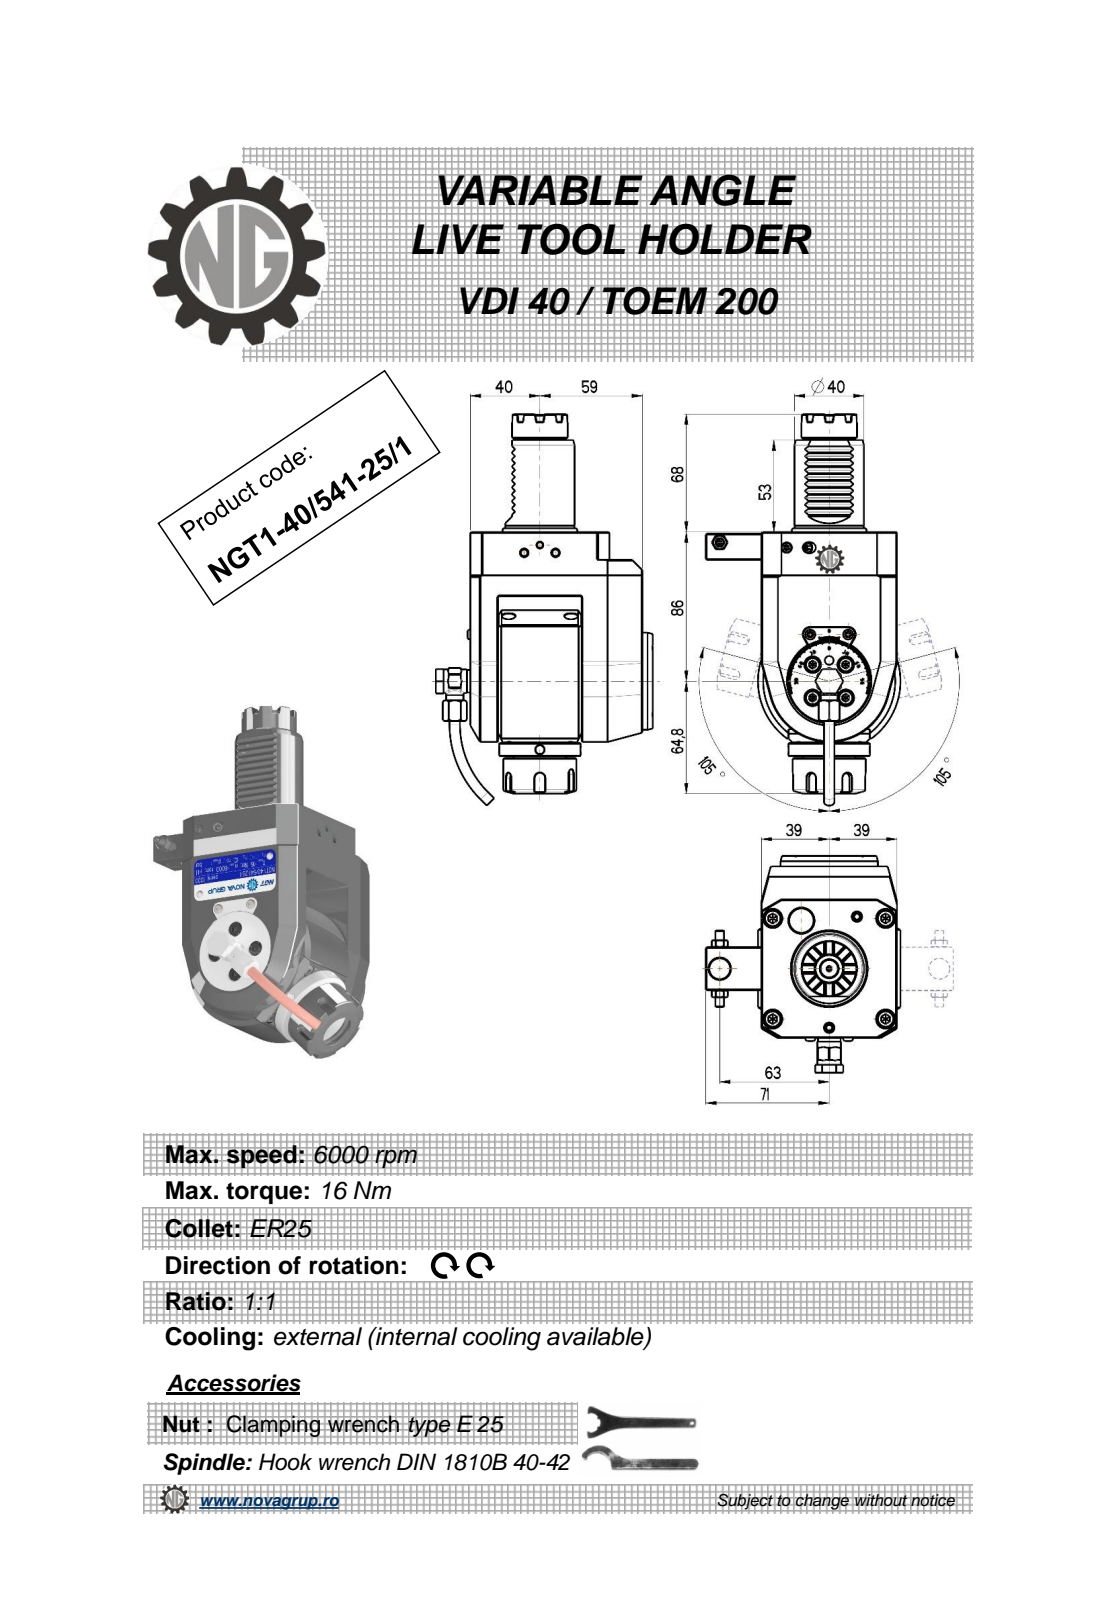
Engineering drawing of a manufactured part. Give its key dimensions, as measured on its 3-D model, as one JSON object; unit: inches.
{"part_name": "NGT1_40_541_25_1", "step_written_by": "PRO/ENGINEER BY PARAMETRIC TECHNOLOGY CORPORATION, 2010280 (CONFIG_CONTROL_DESIGN)", "units": "inches", "bodies": {"solids": 1, "faces": 659, "planar": 284, "cylindrical": 146, "other": 229}, "overall_size": [8.885, 4.917, 4.409], "volume_in3": 55.99, "surface_area_in2": 132.1, "round_holes": [[0.157, 3], [0.197, 2], [0.118, 1], [0.165, 1], [0.244, 1], [0.354, 1], [0.374, 1], [0.433, 1], [0.472, 1], [0.799, 1]], "round_bosses_or_shafts": [[0.394, 2], [0.236, 2], [0.224, 2], [3.228, 1], [2.205, 1], [1.85, 1], [1.654, 1], [1.575, 1]], "partial_cylinders_radius": [[0.01, 12], [0.012, 10], [0.006, 6], [0.118, 5], [0.02, 4], [0.039, 2], [0.394, 2], [0.303, 1]], "face_to_face_distances": [0.63, 1.457, 3.071, 3.898, 2.52, 4.134, 0.236, 0.827, 3.504, 3.268], "hole_center_spacings": [0.016, 1.553, 1.929, 1.945, 2.48, 3.142, 3.152, 4.009]}
